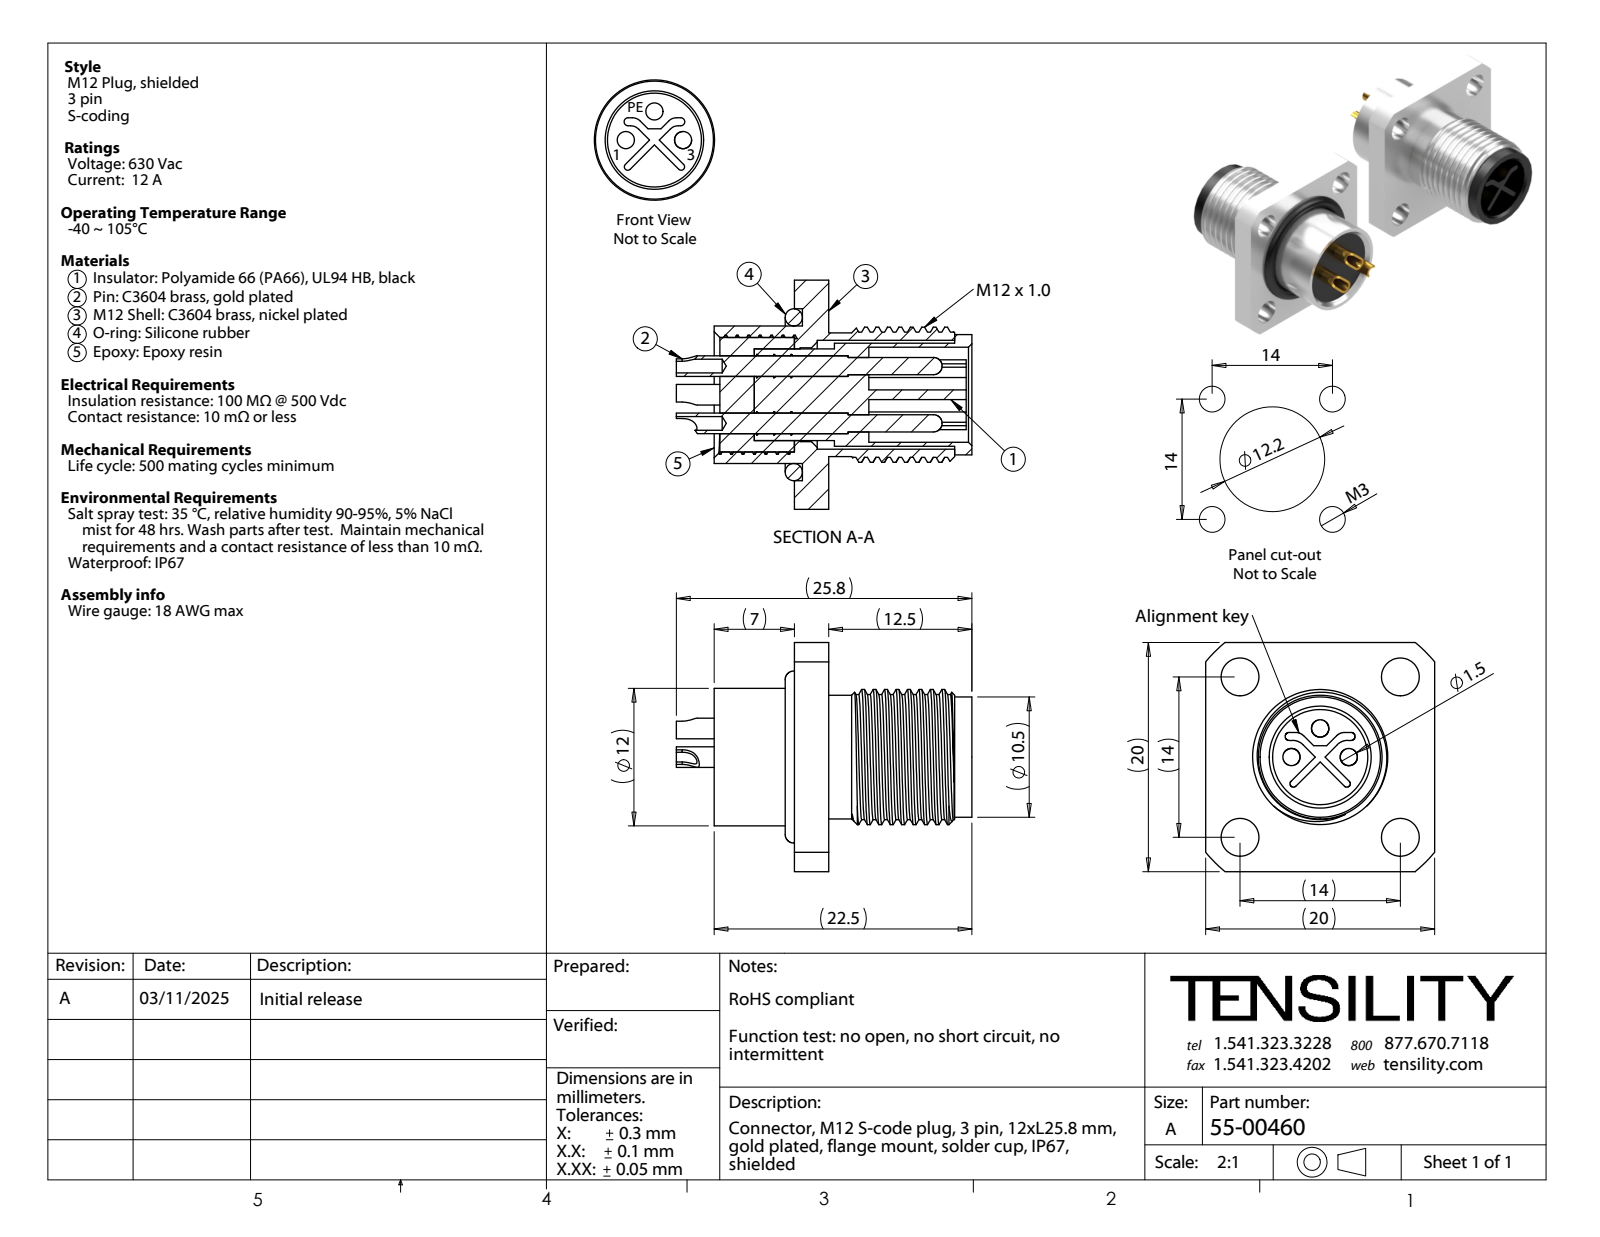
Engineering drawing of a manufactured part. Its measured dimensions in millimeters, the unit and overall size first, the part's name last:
Units: millimetres
Overall size (bounding box): 25.8 × 20 × 20
Round holes (diameter × count): ⌀3.3 ×4, ⌀1.2 ×3, ⌀1.5 ×3, ⌀8 ×1, ⌀8.2 ×1, ⌀8.3 ×1, ⌀9.5 ×1, ⌀10 ×1, ⌀15 ×1
Round bosses / shafts (diameter × count): ⌀1.8 ×3, ⌀12 ×1, ⌀11.8 ×1, ⌀10.92 ×1, ⌀10.8 ×1, ⌀10.5 ×1, ⌀9 ×1
Partial cylindrical surfaces — rounded edges, fillets, slot ends (radius × count): R0.3 ×2, R0.35 ×2, R1 ×2, R1.28 ×2, R1.7 ×2, R13 ×1
Main face-to-face distances: 3, 6.5, 3.5, 20, 10, 0.6, 9.5, 0.7, 2.3, 4.2
Hole centre spacings: 8.32, 11.8, 9.9, 14, 2.5, 3.54, 19.8, 5
Volume: 2 591 mm³ · Surface area: 4 937 mm²
Bodies: 7 solids, 275 faces (59 planar, 157 cylindrical, 59 other)
Part name (STEP PRODUCT): 55-00460-02; 55-00460; 55-00460-03; 55-00460-01 (+2 more)
STEP written by: SolidWorks 2021 (CONFIG_CONTROL_DESIGN)
